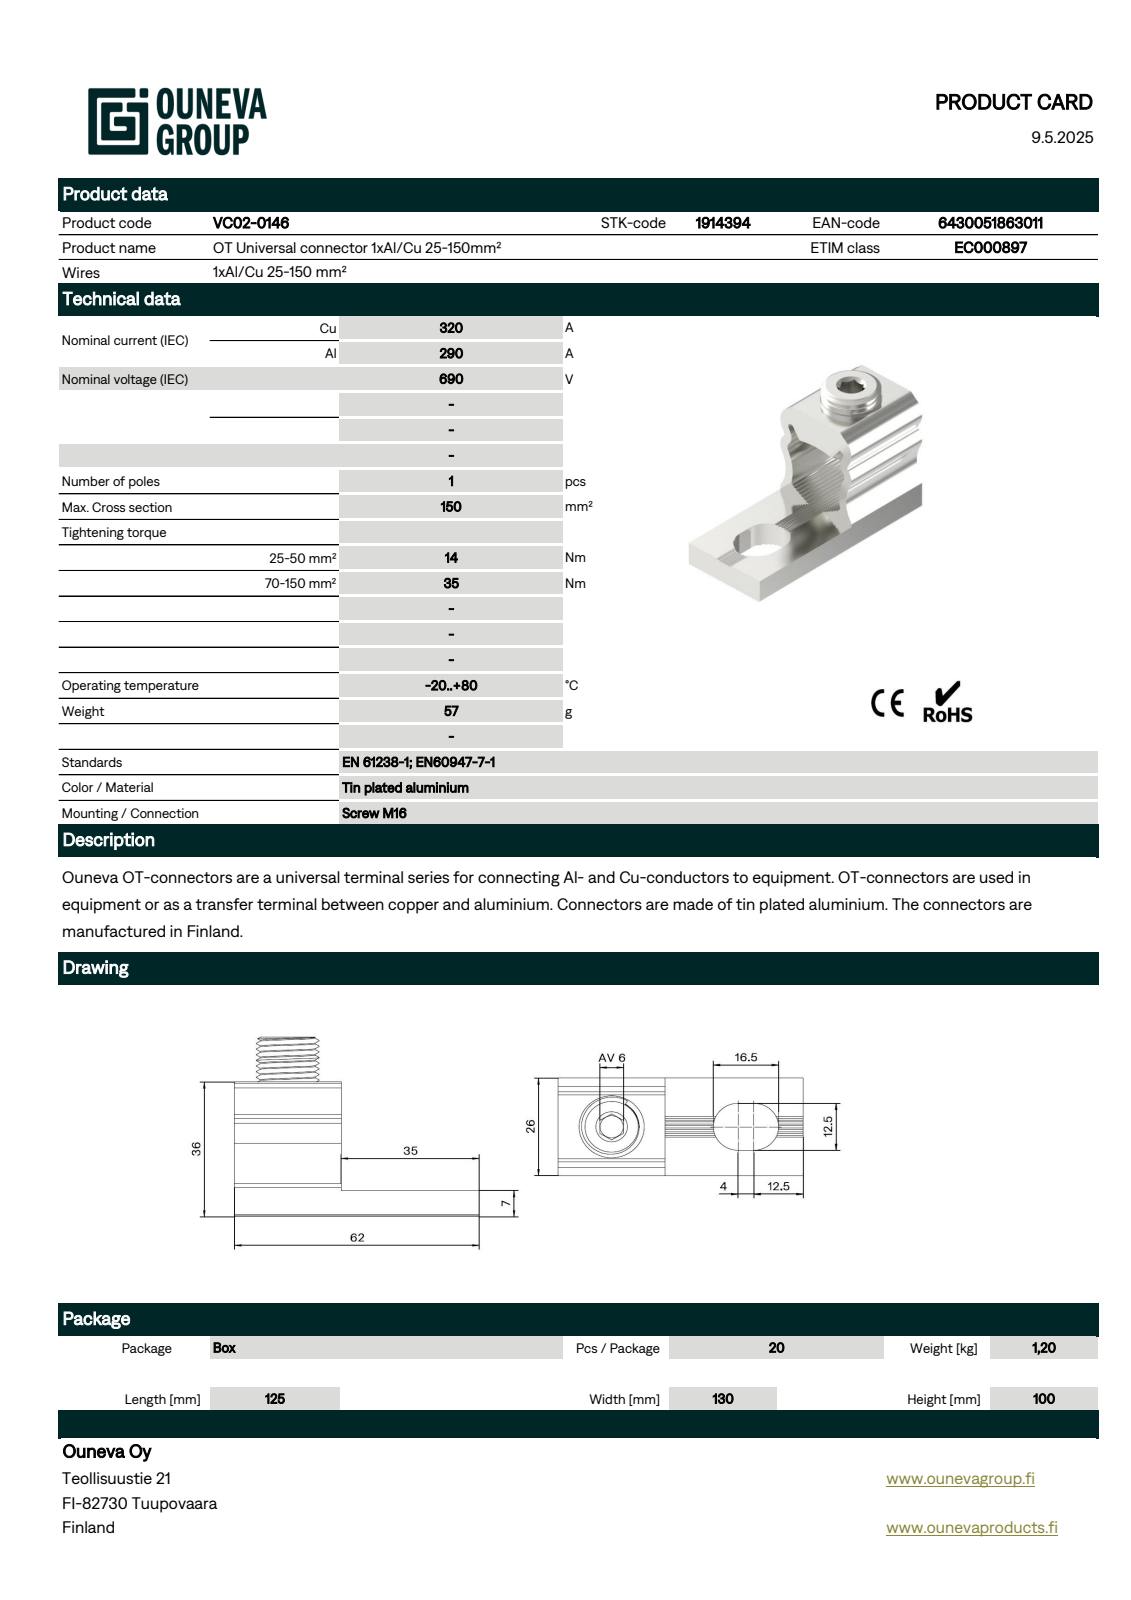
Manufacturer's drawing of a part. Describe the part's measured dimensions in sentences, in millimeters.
The part is named "Liitinrunko_OT_1x150". Its 3-D file was written by "Creo Elements/Direct Modeling 20.6A 14-Oct-2023 (C) Parametric Technology GmbH (AUTOMOTIVE_DESIGN)". It is 1 solid with 272 faces: 101 planar, 163 cylindrical and 8 other. Overall it measures 62 by 47.9 by 26 millimeters. Its volume is 21 146 cubic millimeters and its surface area 10 074 square millimeters. Round bosses or shafts: 1 of diameter 16. Partial cylindrical surfaces (rounded edges, fillets, slot ends): 53 of radius 0.25, 37 of radius 0.3, 10 of radius 1, 2 of radius 0.5, 2 of radius 1.9, 2 of radius 2, 2 of radius 3.6, 2 of radius 4.5. The main face-to-face distances are 26, 27, 1.45, 28.9, 0.72, 2.17, 3.62, 10.86, 62, 35.
